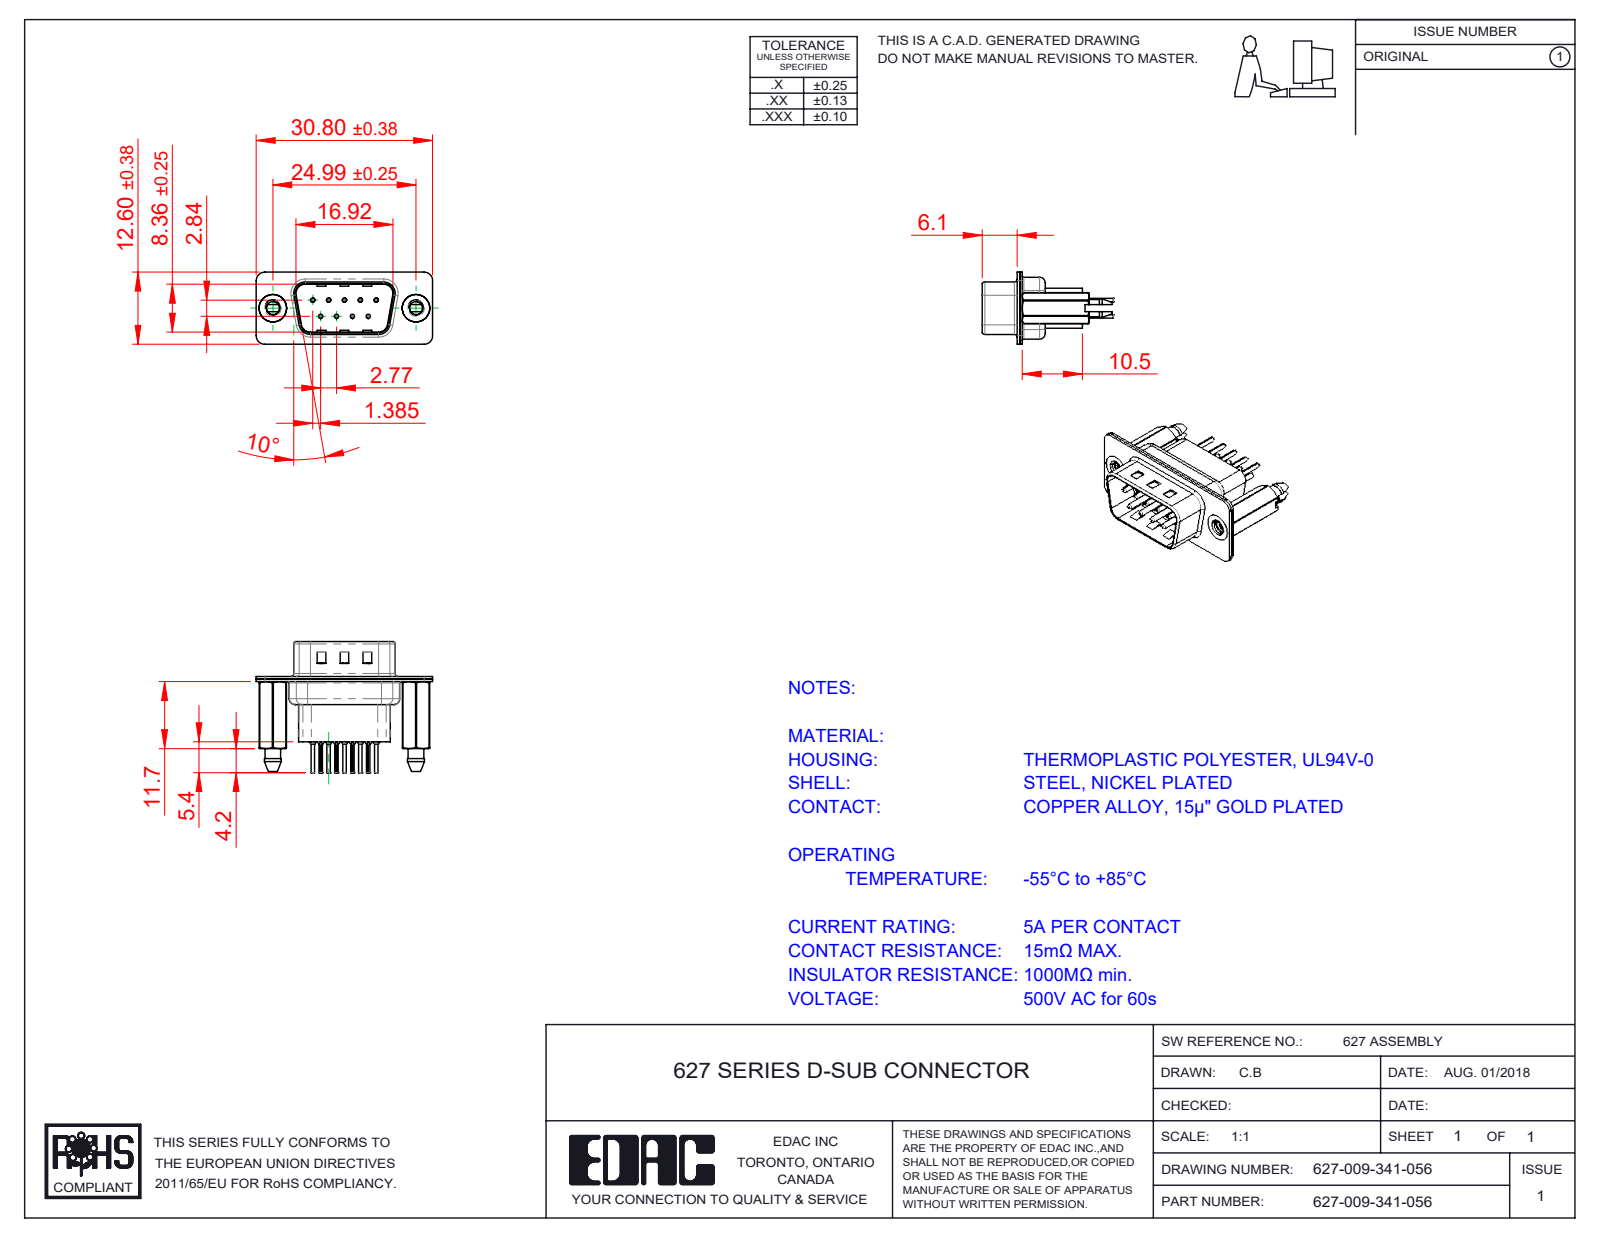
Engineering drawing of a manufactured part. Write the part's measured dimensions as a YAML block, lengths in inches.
part_name: "627-009-341-056; 627 Contact Row 2_41; 627 Housing_09 HP; 627 Shell Rear_09 Contacts (+3 more)"
step_written_by: "SolidWorks 2020 (CONFIG_CONTROL_DESIGN)"
units: inches
bodies: {solids: 14, faces: 1294, planar: 355, cylindrical: 528, other: 411}
overall_size: [1.213, 0.898, 0.496]
volume: 0.125
surface_area: 8.333
round_holes:
  - {diameter: 0.008, count: 9}
  - {diameter: 0.014, count: 9}
  - {diameter: 0.043, count: 9}
  - {diameter: 0.063, count: 9}
  - {diameter: 0.089, count: 2}
  - {diameter: 0.157, count: 2}
  - {diameter: 0.189, count: 2}
round_bosses_or_shafts:
  - {diameter: 0.079, count: 9}
  - {diameter: 0.059, count: 9}
  - {diameter: 0.03, count: 9}
  - {diameter: 0.024, count: 9}
  - {diameter: 0.193, count: 2}
partial_cylinders:
  - {radius: 0.059, count: 20}
  - {radius: 0.004, count: 18}
  - {radius: 0.079, count: 12}
  - {radius: 0.063, count: 10}
  - {radius: 0.02, count: 8}
  - {radius: 0.01, count: 4}
  - {radius: 0.024, count: 4}
  - {radius: 0.026, count: 4}
face_to_face_distances: [0.018, 0.016, 0.035, 0.032, 0.377, 0.055, 0.059, 0.027, 0.302, 0.187]
hole_center_spacings: [0.124, 0.109, 0.218, 0.198, 0.198, 0.327, 0.294, 0.295]
